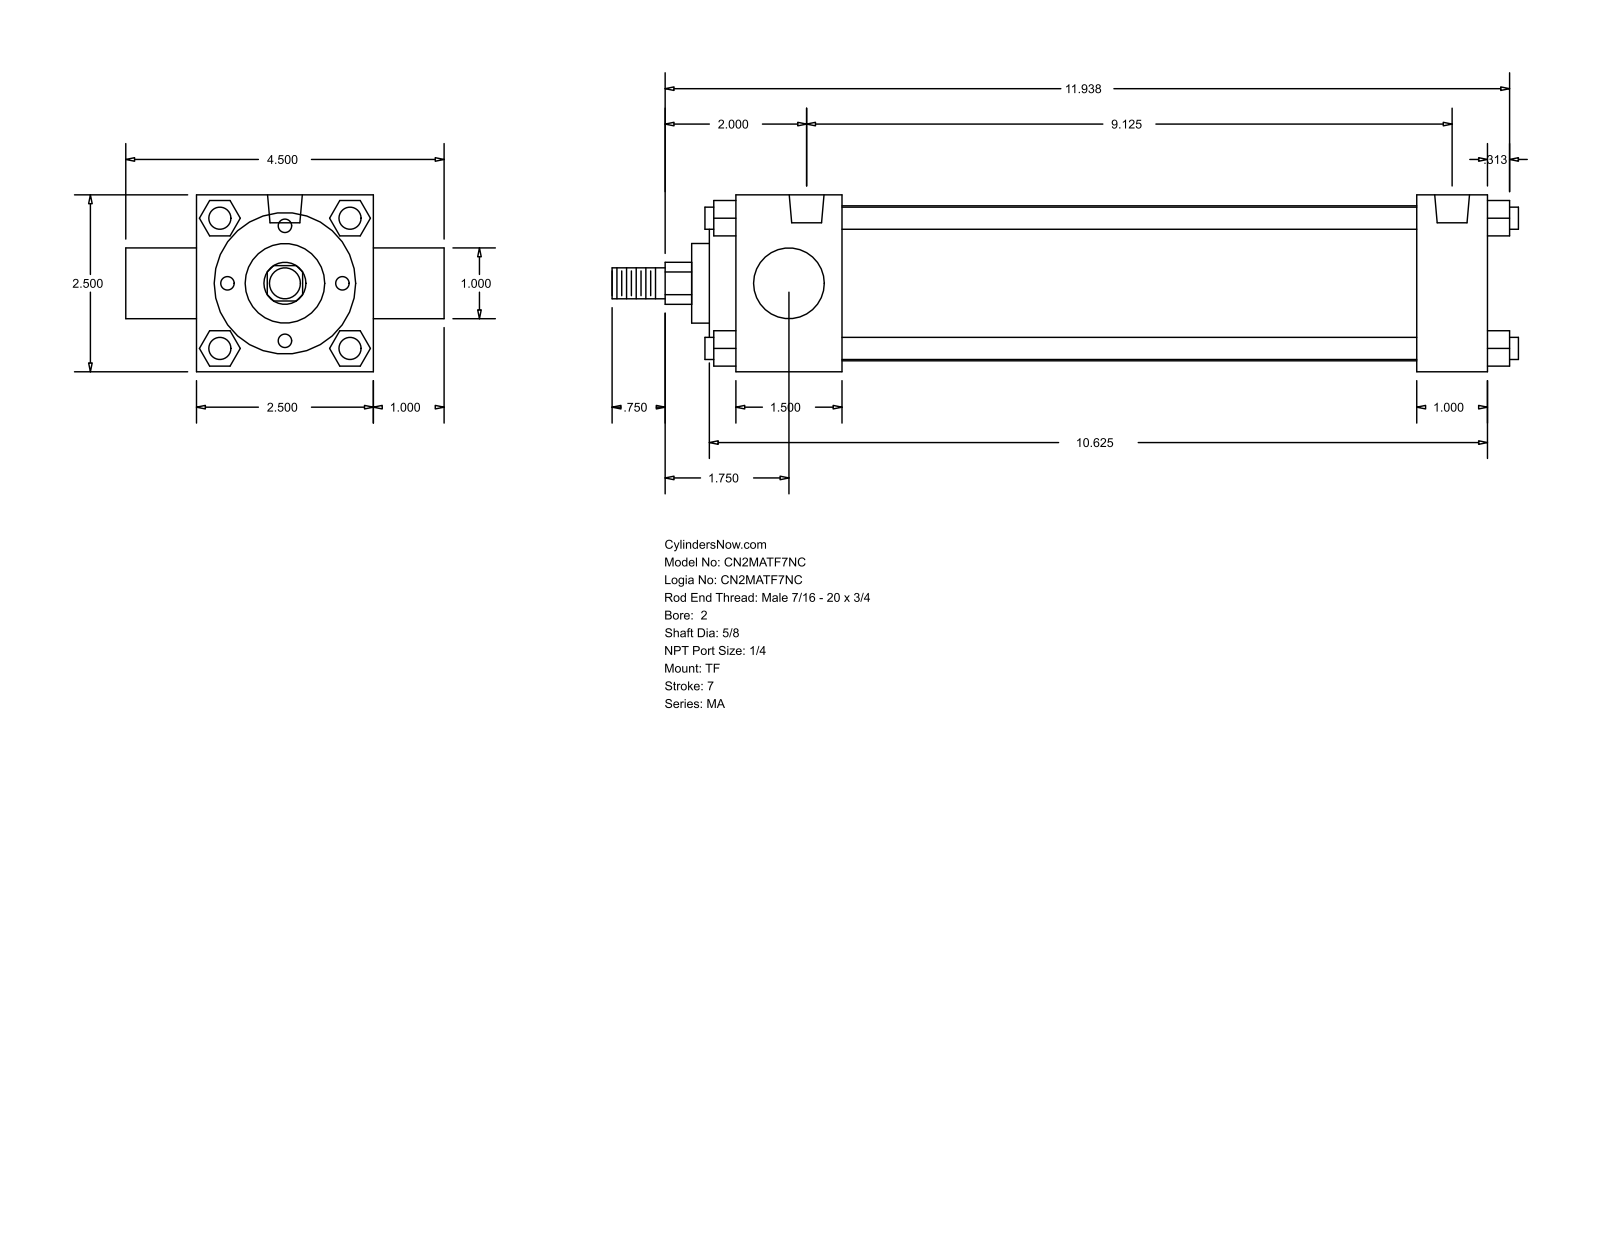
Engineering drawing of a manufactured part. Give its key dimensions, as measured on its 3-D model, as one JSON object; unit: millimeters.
{"part_name": "MA_TF__0200_0.625", "step_written_by": "GSSL Pune (CONFIG_CONTROL_DESIGN)", "units": "millimeters", "bodies": {"solids": 0, "faces": 122, "planar": 93, "cylindrical": 29, "other": 0}, "overall_size": [325.44, 114.3, 63.5], "round_holes": [[7.94, 3], [12.49, 2]], "round_bosses_or_shafts": [[7.94, 4], [55.63, 1], [50.8, 1], [28.57, 1], [25.4, 1], [15.88, 1], [11.11, 1]], "partial_cylinders_radius": [[7.54, 1]], "face_to_face_distances": [63.5, 38.1, 12.7, 269.87, 244.48, 206.38, 231.77, 25.39, 9.52, 47.62], "hole_center_spacings": [231.77]}
